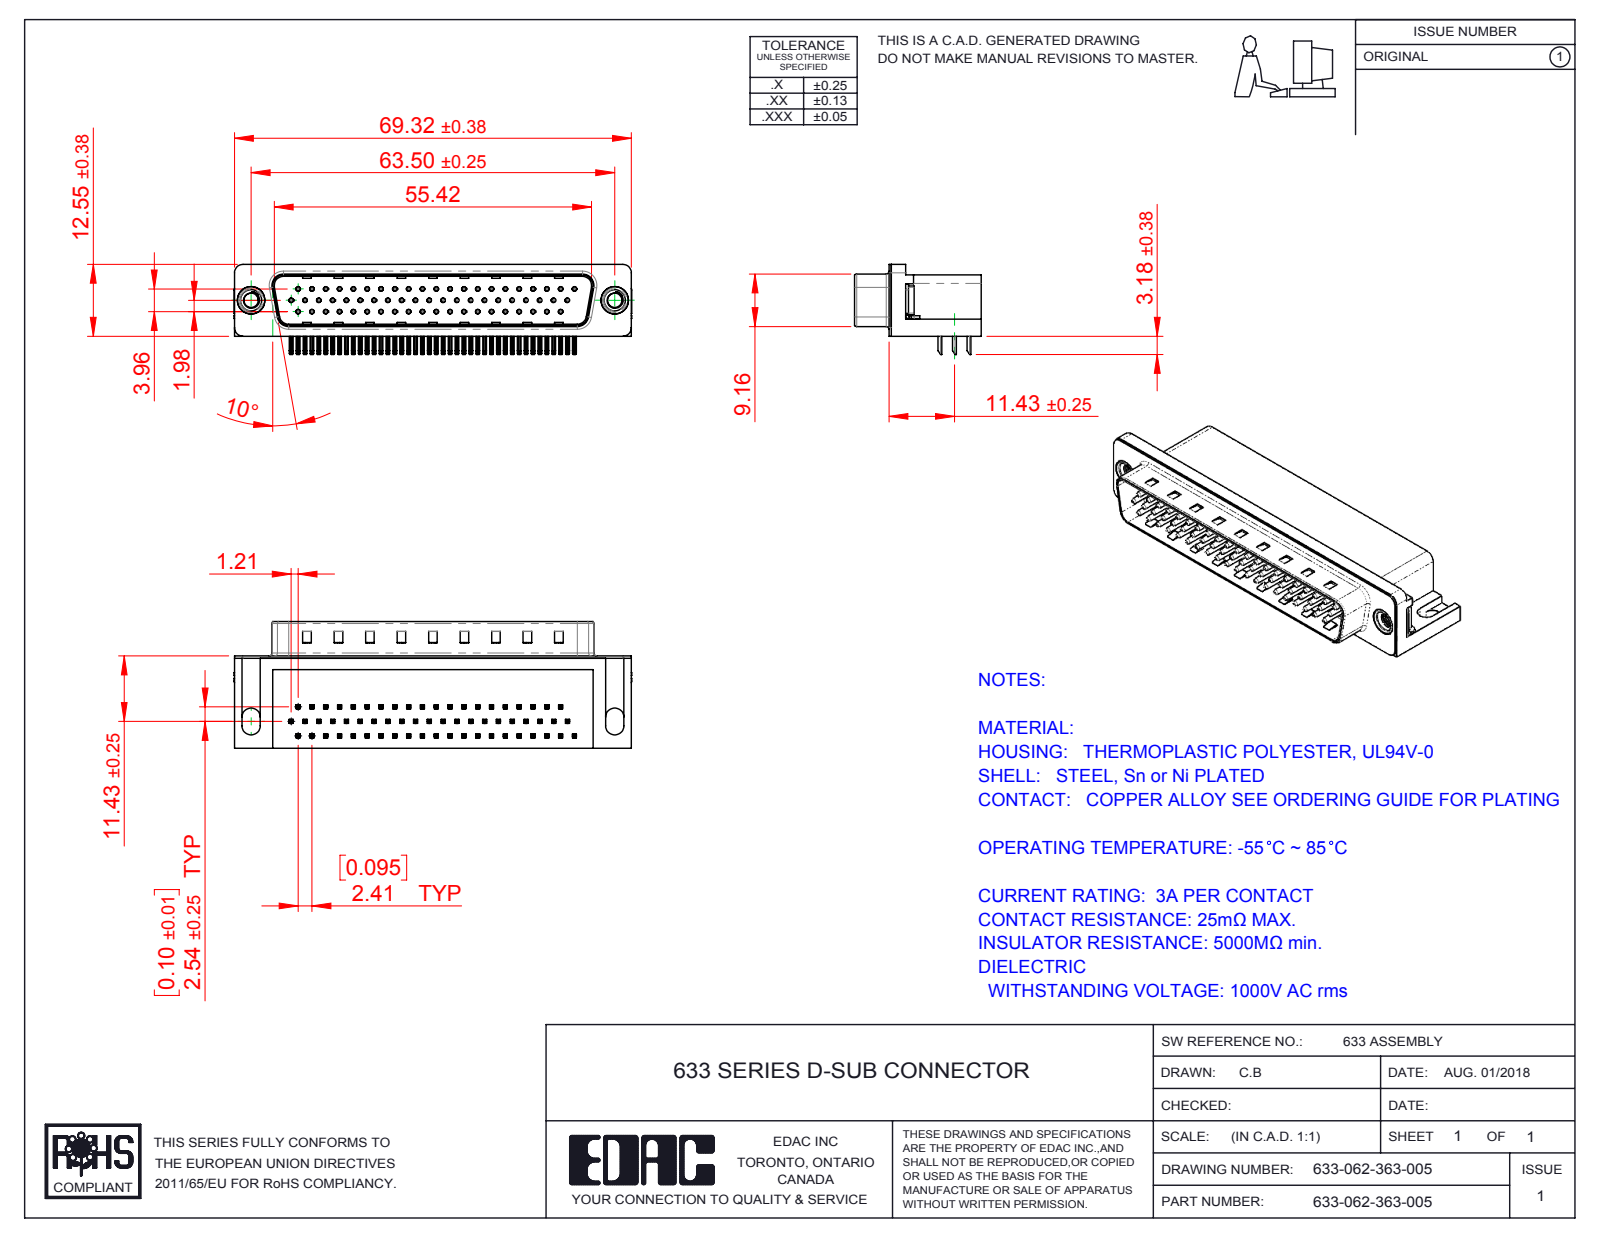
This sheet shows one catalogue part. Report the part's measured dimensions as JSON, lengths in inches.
{"part_name": "633 Shell_62 Contact; 633 Contact Bottom; 633 Contact Middle; 633 M3 Threaded Rivet (+4 more)", "step_written_by": "SolidWorks 2016 (CONFIG_CONTROL_DESIGN)", "units": "inches", "bodies": {"solids": 68, "faces": 5072, "planar": 3213, "cylindrical": 1442, "other": 417}, "overall_size": [2.732, 0.87, 0.619], "volume_in3": 0.671, "surface_area_in2": 20.44, "round_holes": [[0.014, 62], [0.031, 62], [0.098, 2], [0.157, 2], [0.189, 2], [0.197, 2]], "round_bosses_or_shafts": [[0.03, 62], [0.193, 2], [0.187, 2], [0.154, 2]], "partial_cylinders_radius": [[0.01, 256], [0.005, 124], [0.039, 16], [0.02, 9], [0.063, 8], [0.059, 7], [0.035, 4], [0.079, 4]], "face_to_face_distances": [0.016, 0.407, 0.618, 0.345, 0.098, 0.1, 0.114, 0.329, 0.083, 0.339], "hole_center_spacings": [0.095, 0.19, 0.285, 0.38, 0.57, 0.665, 0.19, 0.285]}
